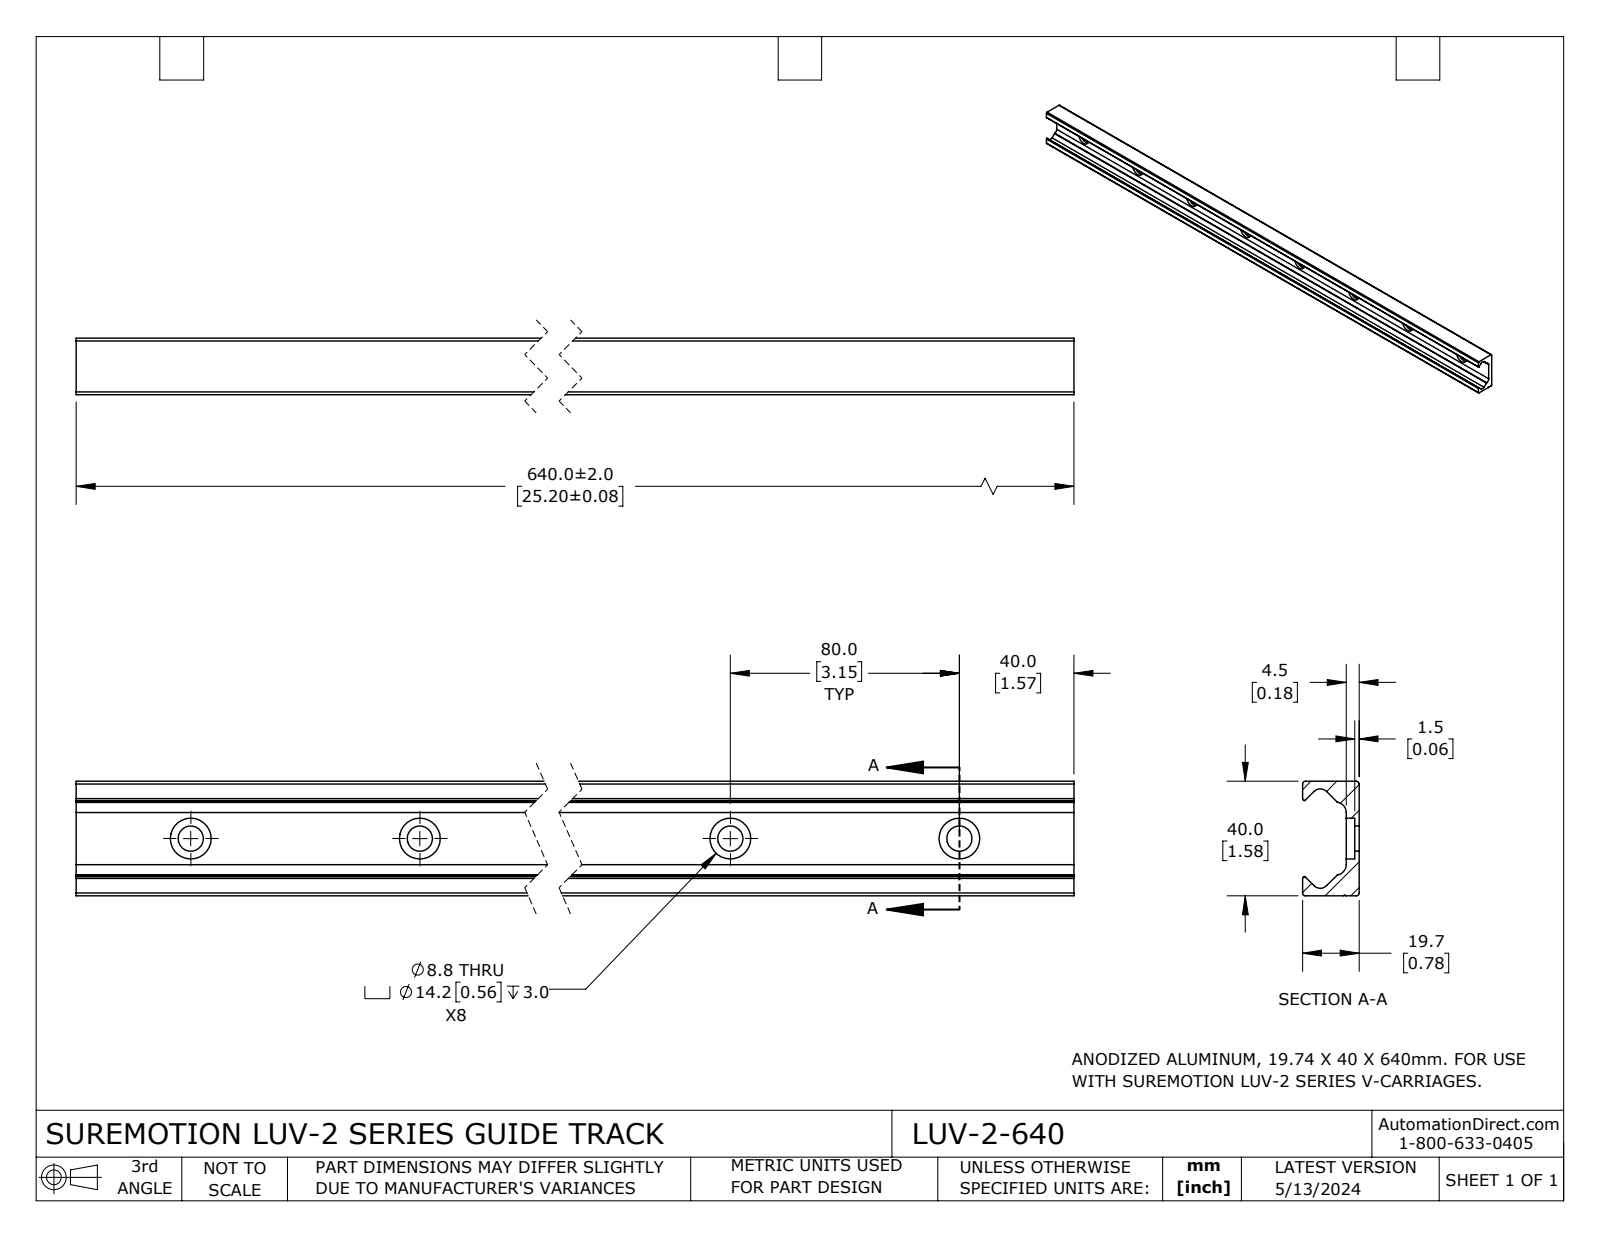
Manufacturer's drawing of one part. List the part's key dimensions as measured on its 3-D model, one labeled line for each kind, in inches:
Part name (STEP PRODUCT): LUV-2-640
STEP written by: SolidWorks 2023 (CONFIG_CONTROL_DESIGN)
Units: inches
Bodies: 1 solid, 68 faces (21 planar, 47 cylindrical, 0 other)
Overall size (bounding box): 25.197 × 1.575 × 0.777
Volume: 13 in³ · Surface area: 151 in²
Round holes (diameter × count): ⌀0.347 ×8, ⌀0.561 ×8
Partial cylindrical surfaces — rounded edges, fillets, slot ends (radius × count): R0.039 ×4, R0.017 ×2, R0.025 ×2, R0.025 ×2, R0.125 ×2, R0.142 ×2, R0.013 ×1
Main face-to-face distances: 1.576, 0.177, 0.777, 0.6, 1.038, 0.059, 0.118, 0.718, 25.197
Hole centre spacings: 3.15, 6.299, 9.449, 12.598, 15.748, 18.898, 22.047
